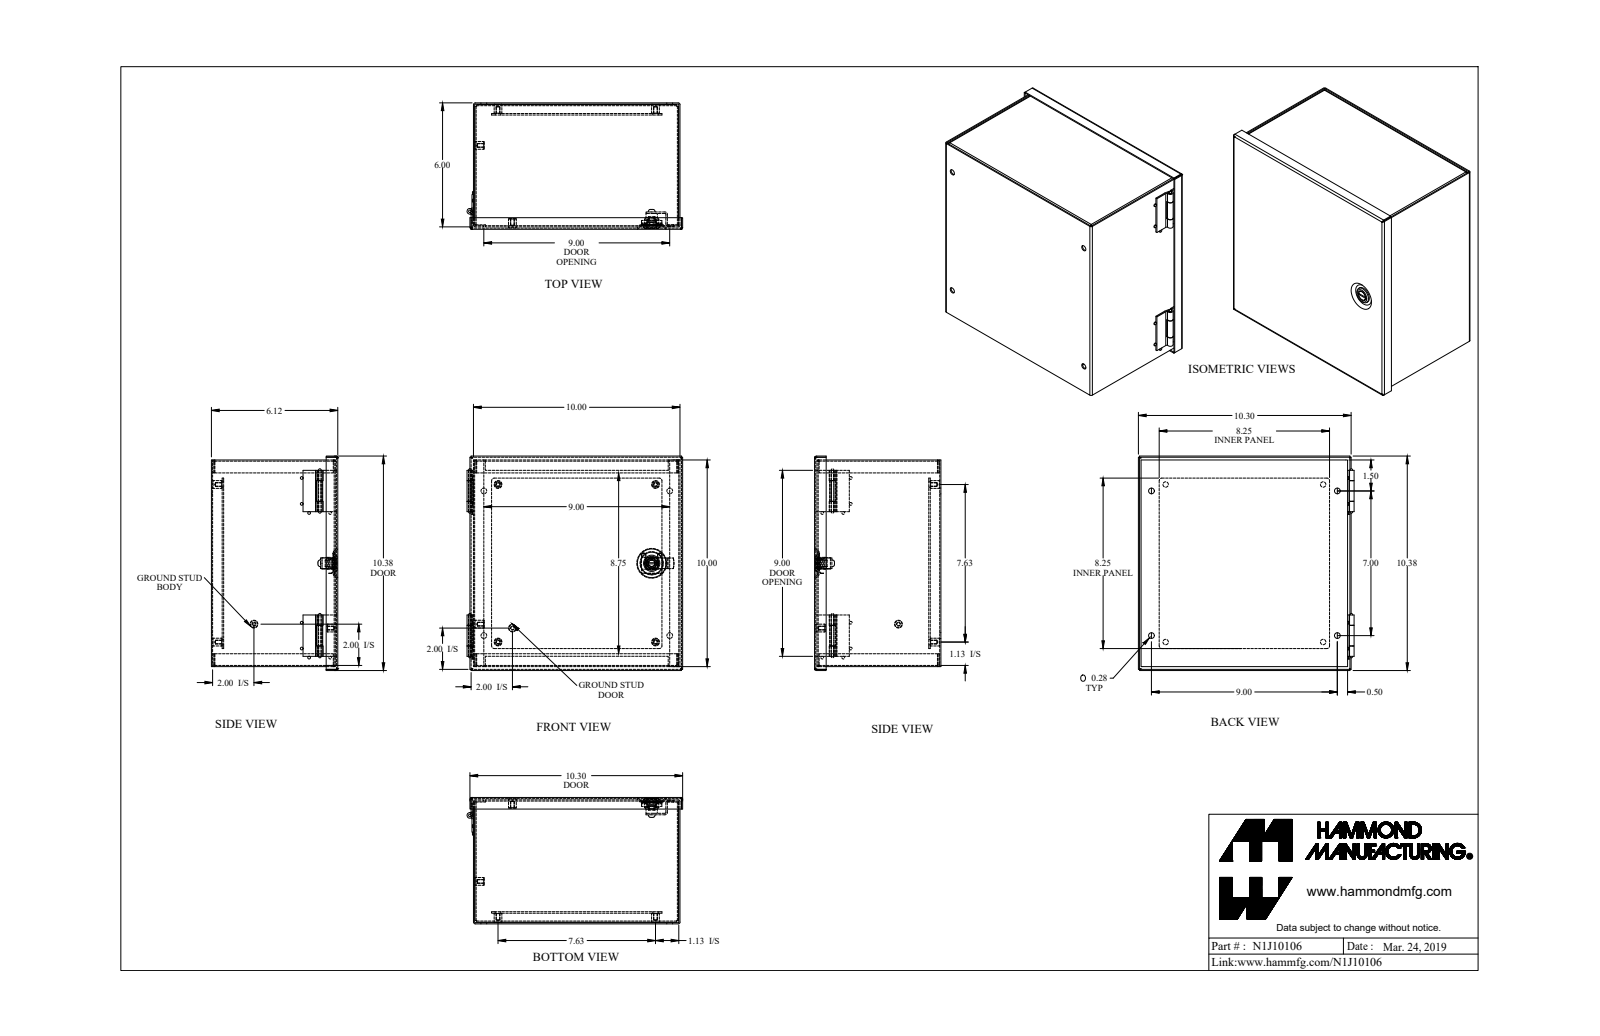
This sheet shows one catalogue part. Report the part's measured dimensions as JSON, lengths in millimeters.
{"part_name": "N1J10106", "step_written_by": "SolidWorks 2018 (AUTOMOTIVE_DESIGN)", "units": "millimeters", "bodies": {"solids": 18, "faces": 477, "planar": 224, "cylindrical": 188, "other": 65}, "overall_size": [265.3, 263.7, 155.4], "volume_mm3": 566800, "surface_area_mm2": 761900, "round_holes": [[4, 6], [6.7, 4], [7.1, 4], [3.2, 1], [8.1, 1], [12.1, 1]], "round_bosses_or_shafts": [[3.3, 8], [9.5, 6], [20, 1], [13.9, 1], [12, 1], [11.9, 1], [9.3, 1], [8.1, 1]], "partial_cylinders_radius": [[0.7, 16], [2.2, 16], [0.3, 4], [2.5, 4], [3.2, 4], [0.9, 2], [2, 2], [6.4, 2]], "face_to_face_distances": [1.4, 252.6, 153.9, 254, 251.1, 152.5, 155.4, 1.8, 13.1, 11.7], "hole_center_spacings": [19.2, 186.6, 193.7, 211.3, 281.2, 91.6, 97, 177.8]}
